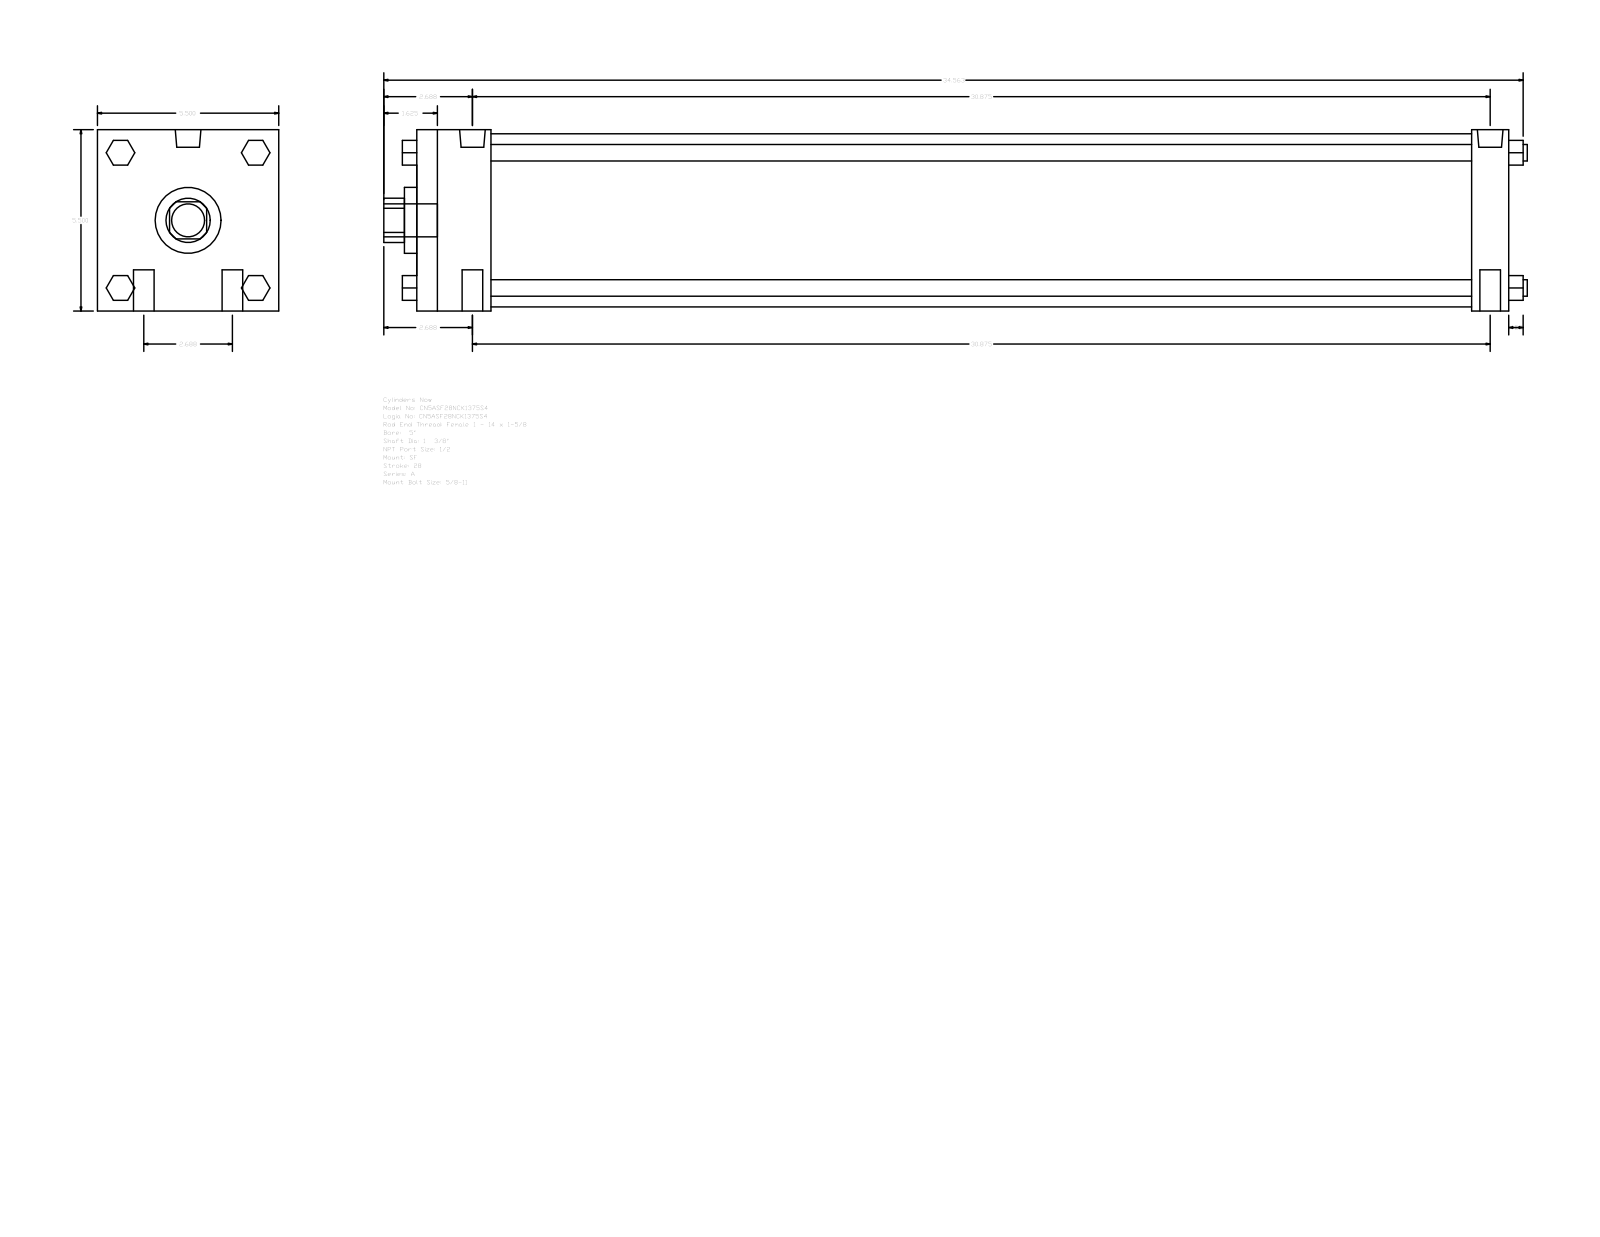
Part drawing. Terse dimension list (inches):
name: A_SF__0500_1.375
written by: GSSL Pune (CONFIG_CONTROL_DESIGN)
unit: in
bodies: 0 solids, 124 faces (94 planar, 30 cylindrical, 0 other)
size: 34.687 × 5.5 × 5.5
holes: 1× ⌀1.375, 1× ⌀2, 1× ⌀5.25
bosses: 4× ⌀0.625, 4× ⌀0.5, 2× ⌀0.778, 2× ⌀0.344, 1× ⌀1
rounds: 1× R0.672
face distances: 5.5, 33.125, 1.125, 2.25, 32, 29.75, 30.875, 0.75, 2.05, 3.55
